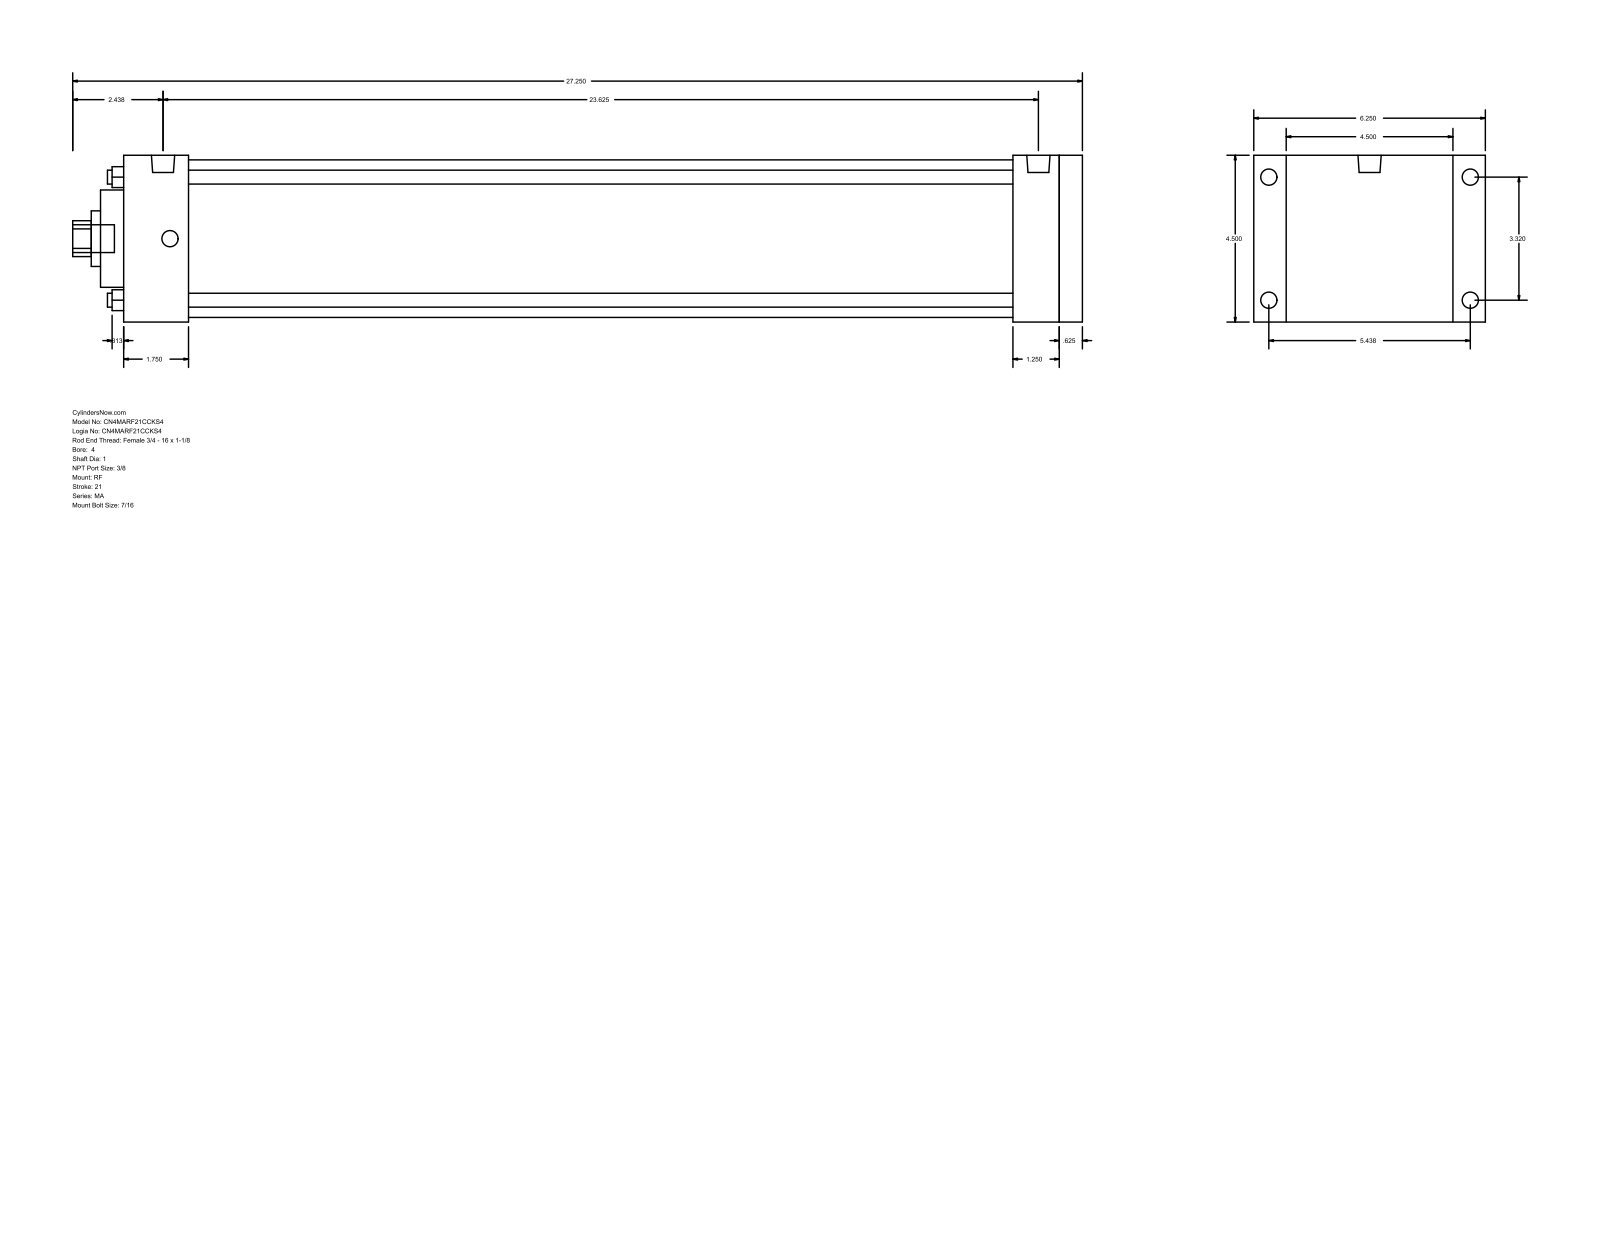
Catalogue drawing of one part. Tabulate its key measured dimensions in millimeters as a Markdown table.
| quantity | value |
| --- | --- |
| part name | MA_RF__0400_1 |
| STEP written by | GSSL Pune (CONFIG_CONTROL_DESIGN) |
| units | millimeters |
| bodies | 0 solids, 94 faces (65 planar, 29 cylindrical, 0 other) |
| overall size | 692.15 × 158.75 × 114.3 |
| round holes (diameter × count) | 9.53 × 4, 25.4 × 1, 38.1 × 1, 66.67 × 1, 107.95 × 1 |
| round bosses / shafts (diameter × count) | 11.11 × 8, 15.93 × 2, 19.05 × 1 |
| partial cylindrical surfaces (radius × count) | 12.29 × 1 |
| main face-to-face distances | 114.3, 657.23, 641.35, 15.88, 22.23, 136.53, 609.6, 31.75, 47.63, 44.46 |
| hole center spacings | 59.62, 84.32, 119.25 |
